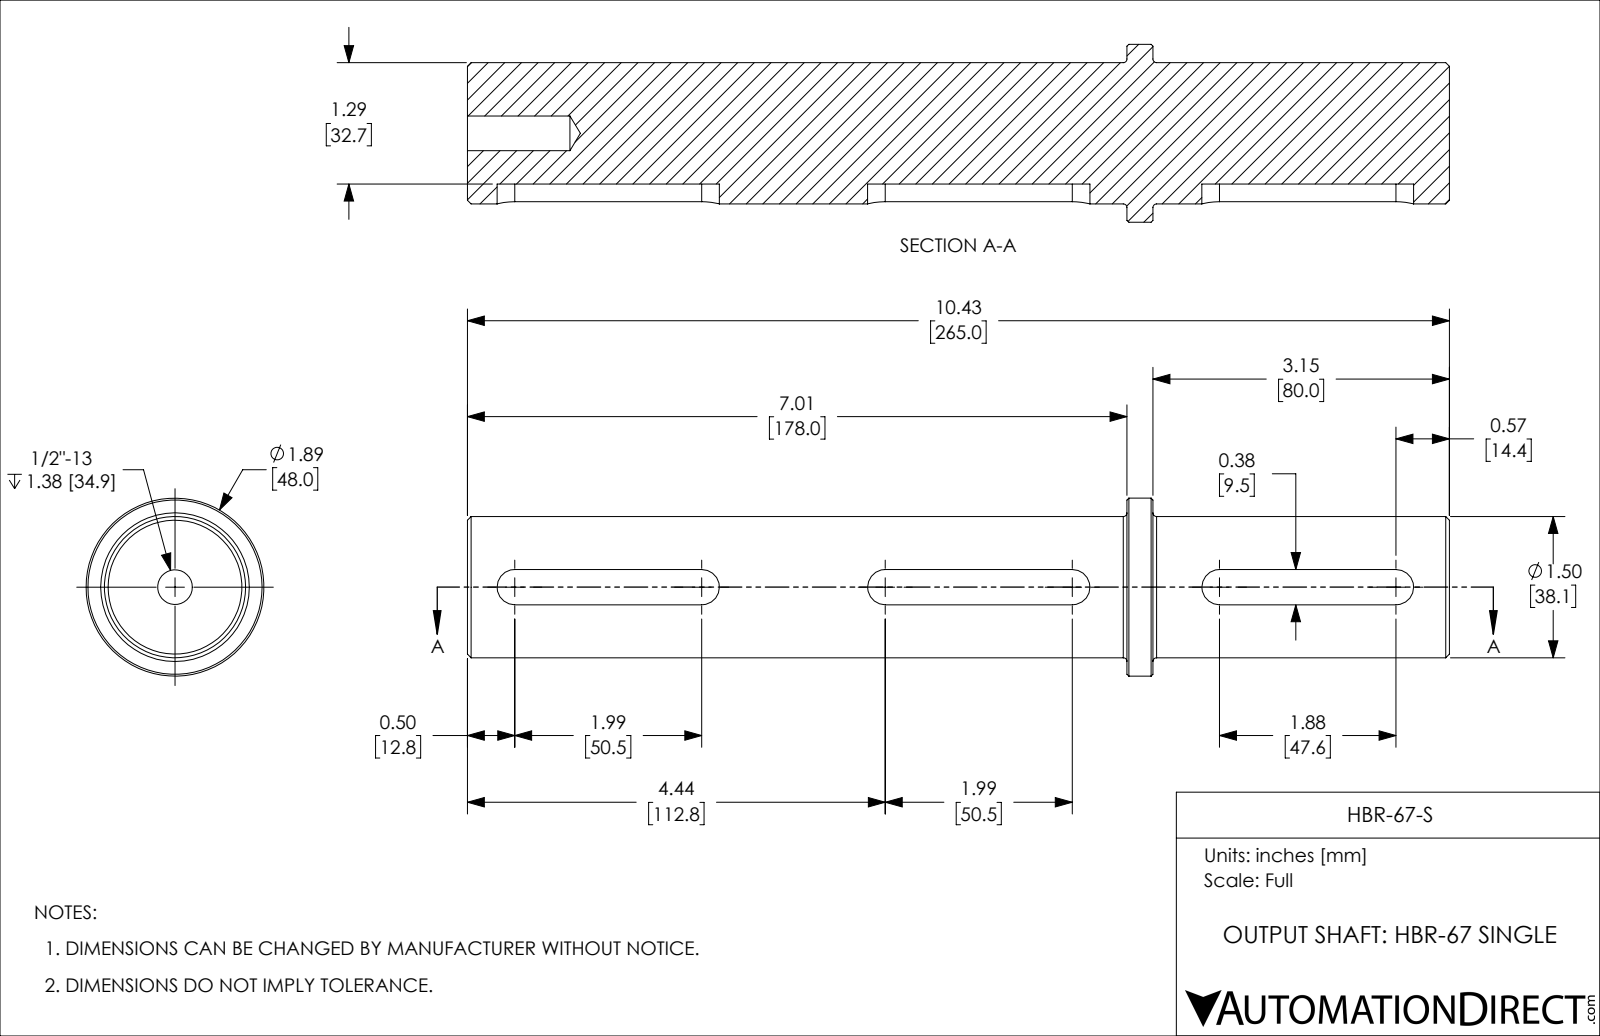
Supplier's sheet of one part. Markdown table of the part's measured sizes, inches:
| quantity | value |
| --- | --- |
| part name | HBR-67-S |
| STEP written by | SolidWorks 2018 (AUTOMOTIVE_DESIGN) |
| units | inches |
| bodies | 1 solid, 44 faces (13 planar, 17 cylindrical, 14 other) |
| overall size | 10.433 × 1.89 × 1.89 |
| volume | 18.08 in³ |
| surface area | 58.74 in² |
| round holes (diameter × count) | 0.368 × 1 |
| round bosses / shafts (diameter × count) | 1.89 × 1, 1.5 × 1 |
| partial cylindrical surfaces (radius × count) | 0.188 × 5, 0.187 × 1 |
| main face-to-face distances | 10.433, 0.375, 7.008, 3.426, 7.283, 0.276, 3.15 |
